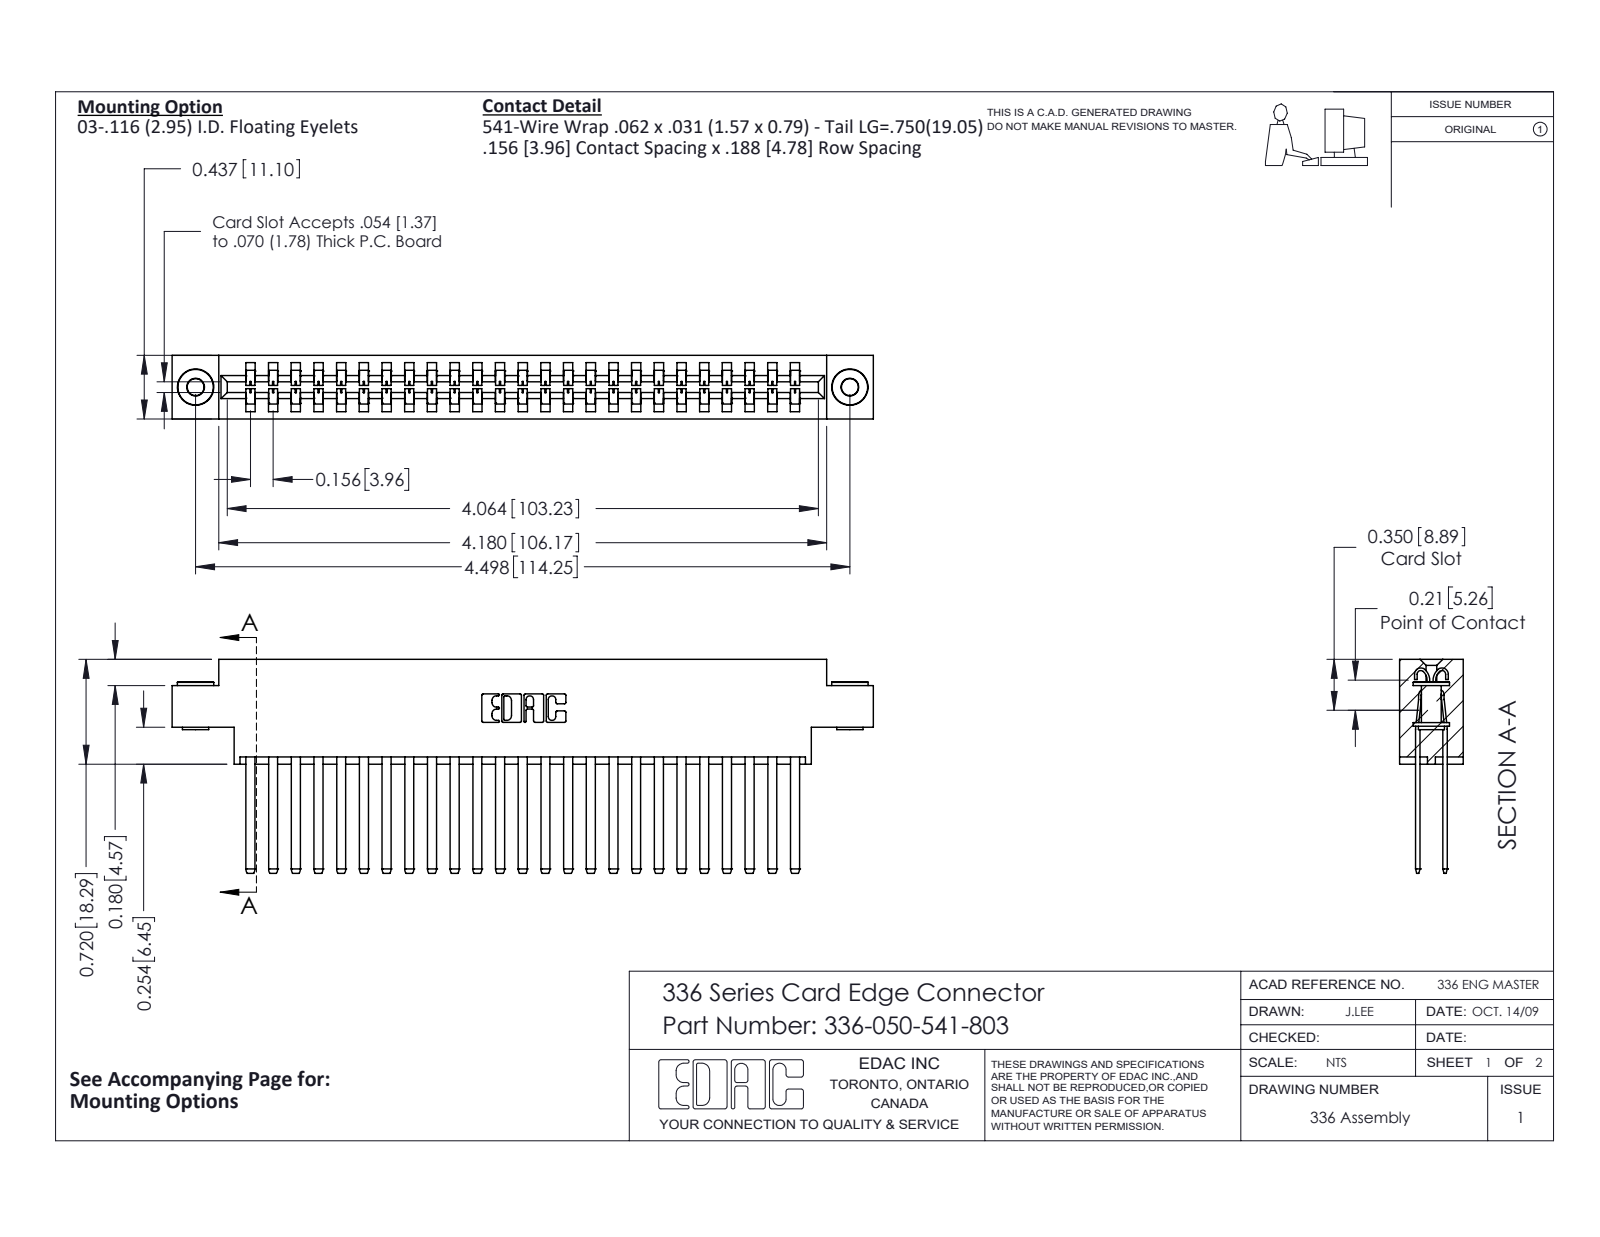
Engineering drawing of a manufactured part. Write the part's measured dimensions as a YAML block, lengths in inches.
part_name: "345-250-002_345-250-002-102; 336 Part_Offset - .156 Dia - TH; 336-050-541-803; 336-290-001_336-290-541"
step_written_by: "SolidWorks 2020 (CONFIG_CONTROL_DESIGN)"
units: inches
bodies: {solids: 53, faces: 2256, planar: 1384, cylindrical: 864, other: 8}
overall_size: [4.821, 1.47, 0.437]
volume: 1.122
surface_area: 36.39
round_holes:
  - {diameter: 0.116, count: 2}
  - {diameter: 0.156, count: 2}
round_bosses_or_shafts:
  - {diameter: 0.25, count: 2}
  - {diameter: 0.18, count: 2}
  - {diameter: 0.136, count: 2}
partial_cylinders:
  - {radius: 0.004, count: 100}
  - {radius: 0.056, count: 50}
  - {radius: 0.01, count: 22}
  - {radius: 0.007, count: 6}
  - {radius: 0.031, count: 6}
  - {radius: 0.022, count: 4}
  - {radius: 0.04, count: 4}
  - {radius: 0.026, count: 3}
face_to_face_distances: [0.188, 0.031, 0.328, 0.14, 0.297, 0.109, 0.437, 0.033, 0.181, 0.256]
hole_center_spacings: [4.498]
